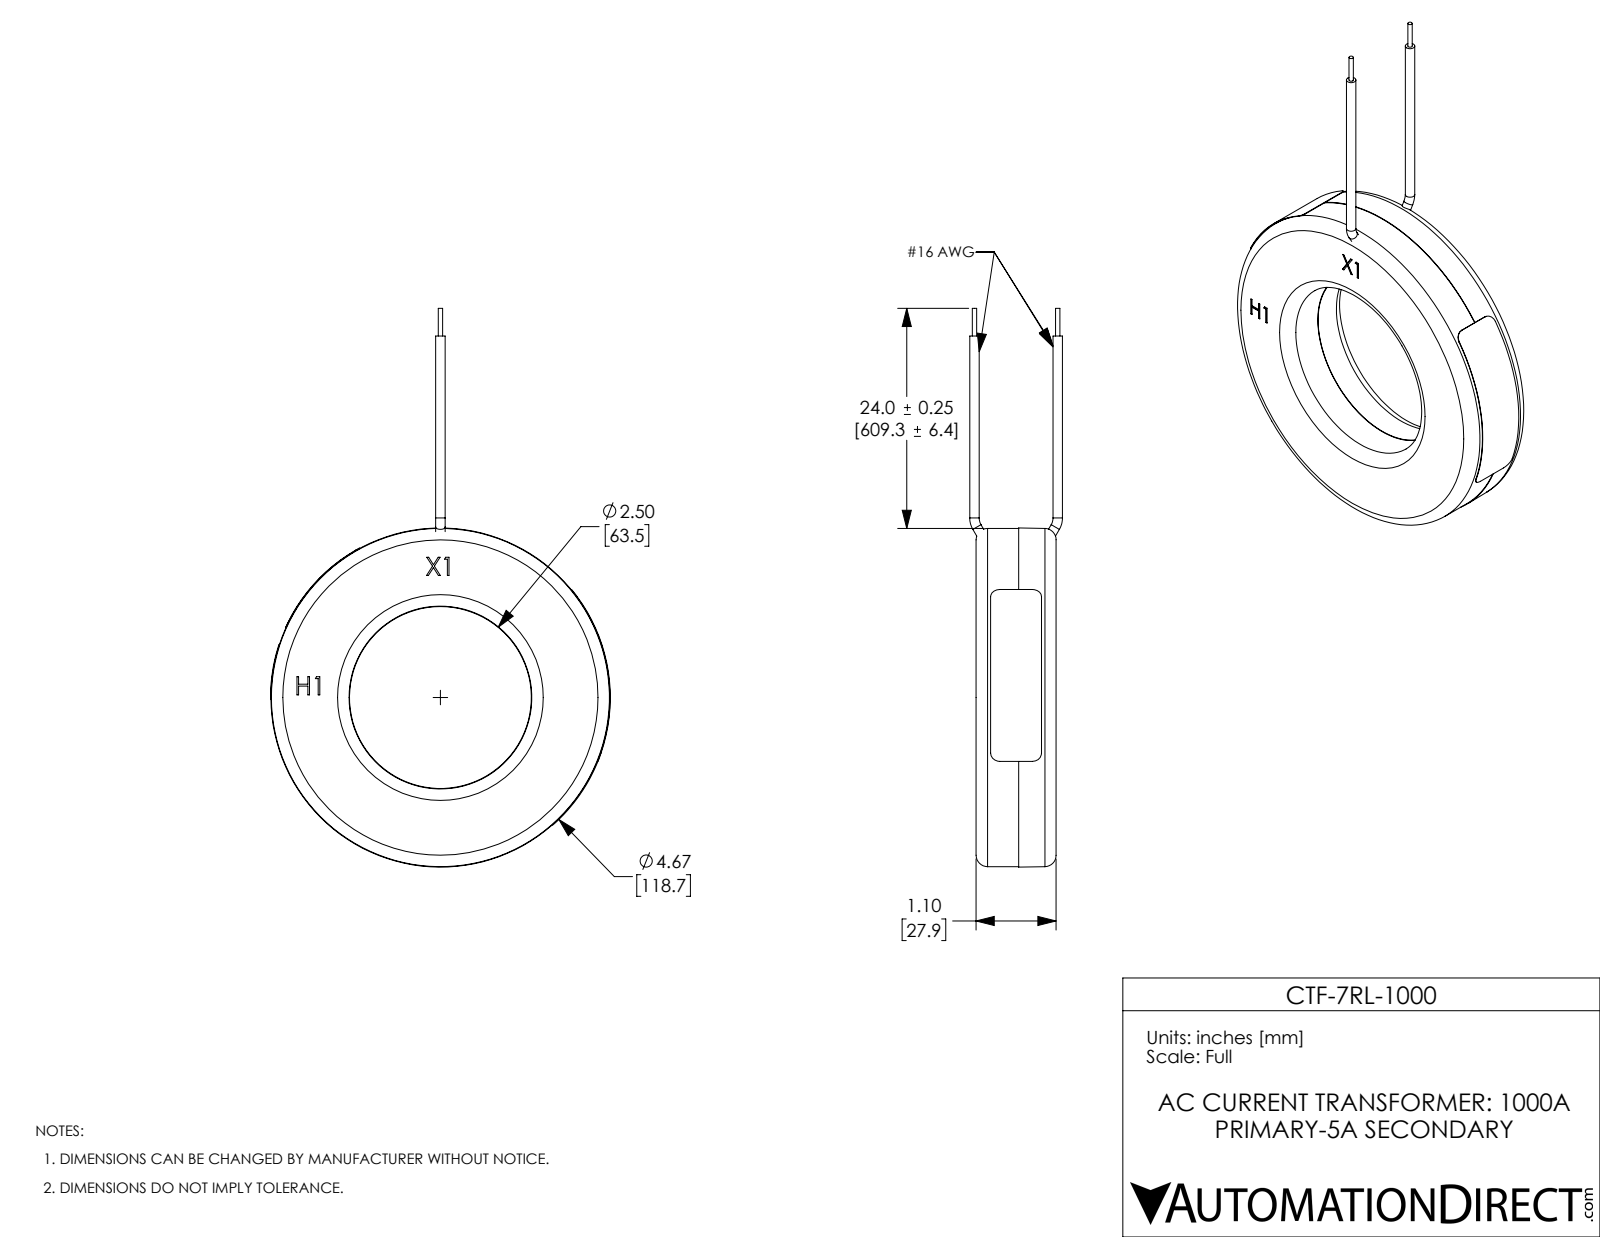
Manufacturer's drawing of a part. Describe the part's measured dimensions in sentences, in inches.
The part is named "CTF-7RL-1000". Its 3-D file was written by "SolidWorks 2018 (AUTOMOTIVE_DESIGN)". It is 6 solids with 114 faces: 62 planar, 31 cylindrical and 21 other. Overall it measures 7.679 by 4.673 by 1.275 inches. Its volume is 13.1 cubic inches and its surface area 79.58 square inches. Round holes: 1 of diameter 2.513. Round bosses or shafts: 4 of diameter 0.13, 2 of diameter 0.06, 1 of diameter 4.648. Partial cylindrical surfaces (rounded edges, fillets, slot ends): 4 of radius 0.06, 4 of radius 0.125, 1 of radius 2.33, 1 of radius 2.33, 1 of radius 2.331, 1 of radius 2.336. The main face-to-face distances are 0.515, 1.1, 0.585, 1.09, 0.575, 0.2, 0.9, 0.315, 0.89, 0.7.
